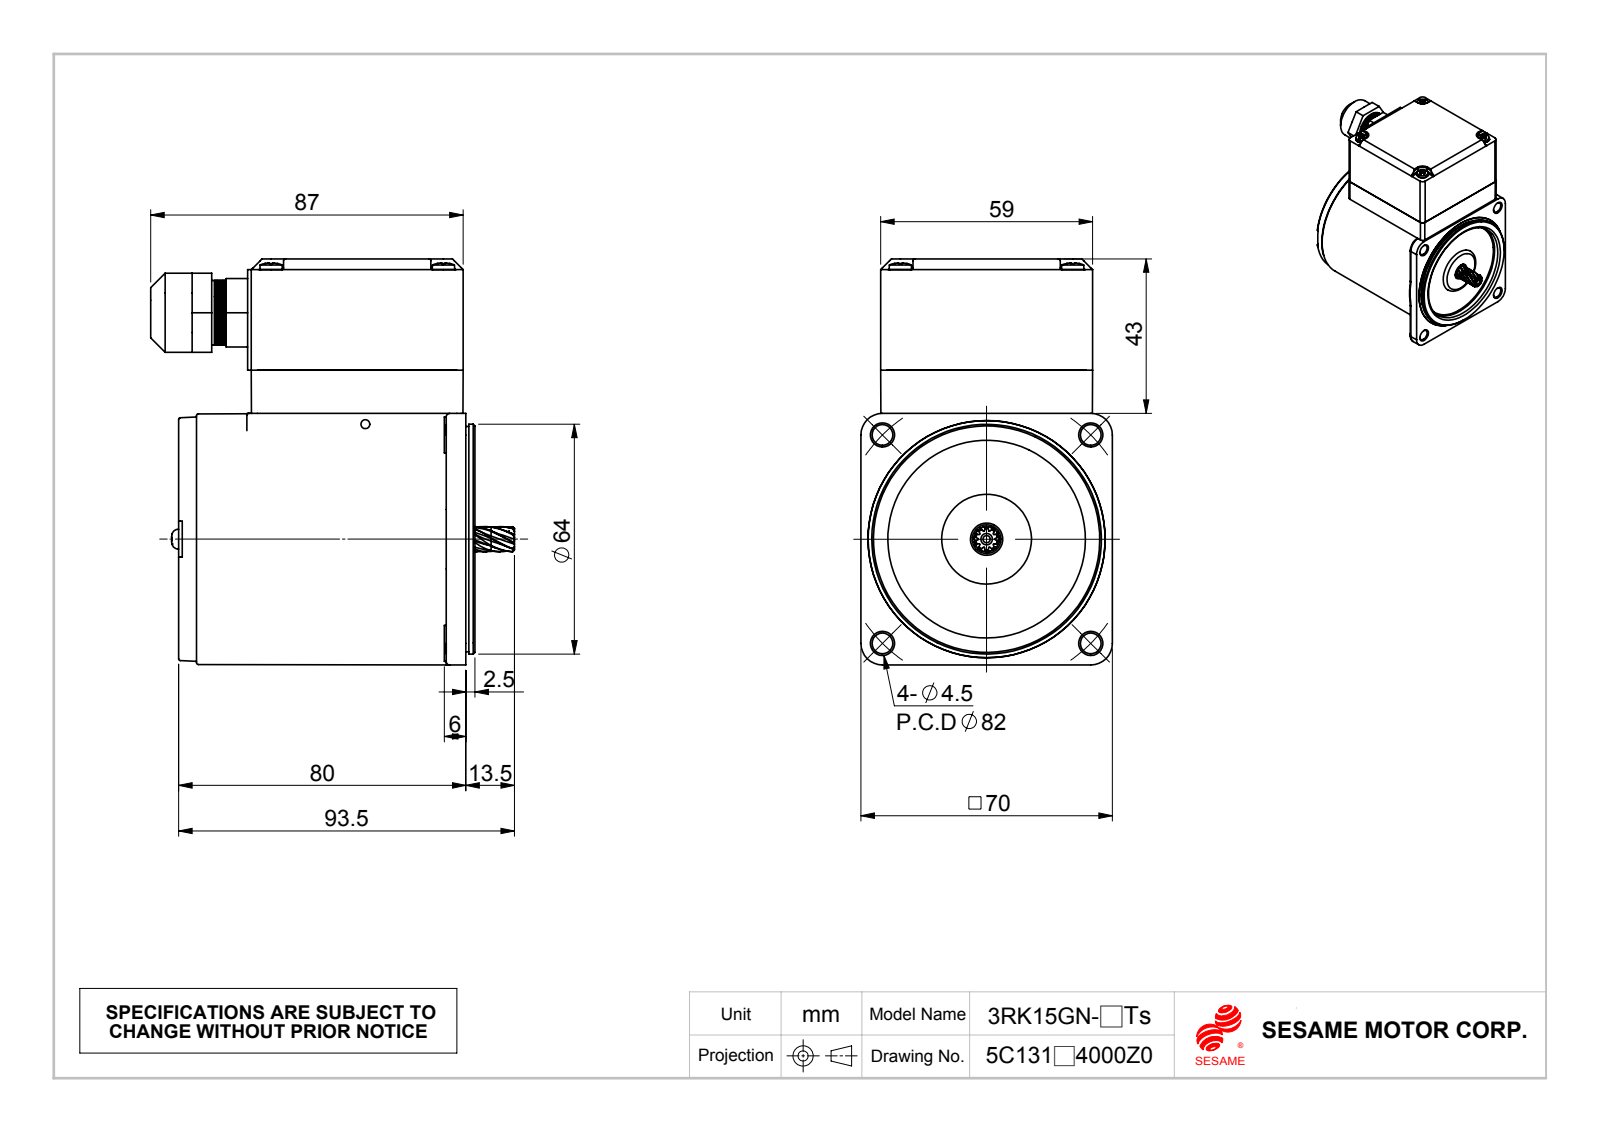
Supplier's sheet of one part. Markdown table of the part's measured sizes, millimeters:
| quantity | value |
| --- | --- |
| part name | M315Ts-RK_3.鑽孔; Ts下墊片; C364_車工(成品); 15GN_0.成品 (+2 more) |
| STEP written by | SolidWorks 2010 (CONFIG_CONTROL_DESIGN) |
| units | millimeters |
| bodies | 14 solids, 2620 faces (247 planar, 895 cylindrical, 1478 other) |
| overall size | 113 × 101.25 × 70 |
| volume | 226 685 mm³ |
| surface area | 91 933 mm² |
| round holes (diameter × count) | 3.3 × 4, 3.5 × 4, 3.9 × 4, 4.2 × 4, 4.3 × 4, 5.75 × 4, 2.5 × 3, 4 × 2, 2 × 1, 9 × 1, 11 × 1, 12 × 1 |
| round bosses / shafts (diameter × count) | 3 × 6, 10 × 4, 6.3 × 4, 5.5 × 2, 63.93 × 1, 62.73 × 1, 57.42 × 1, 57.2 × 1 |
| partial cylindrical surfaces (radius × count) | 0.5 × 13, 2 × 12, 0.3 × 8, 1 × 8, 5 × 8, 4 × 6, 1.5 × 4, 2.75 × 4 |
| main face-to-face distances | 12, 0.75, 4, 1, 3, 1.5, 31, 43, 77.5, 74.5 |
| hole center spacings | 43.34, 14, 10.72, 19.8, 25.87, 27.01, 32.65, 41.01 |
